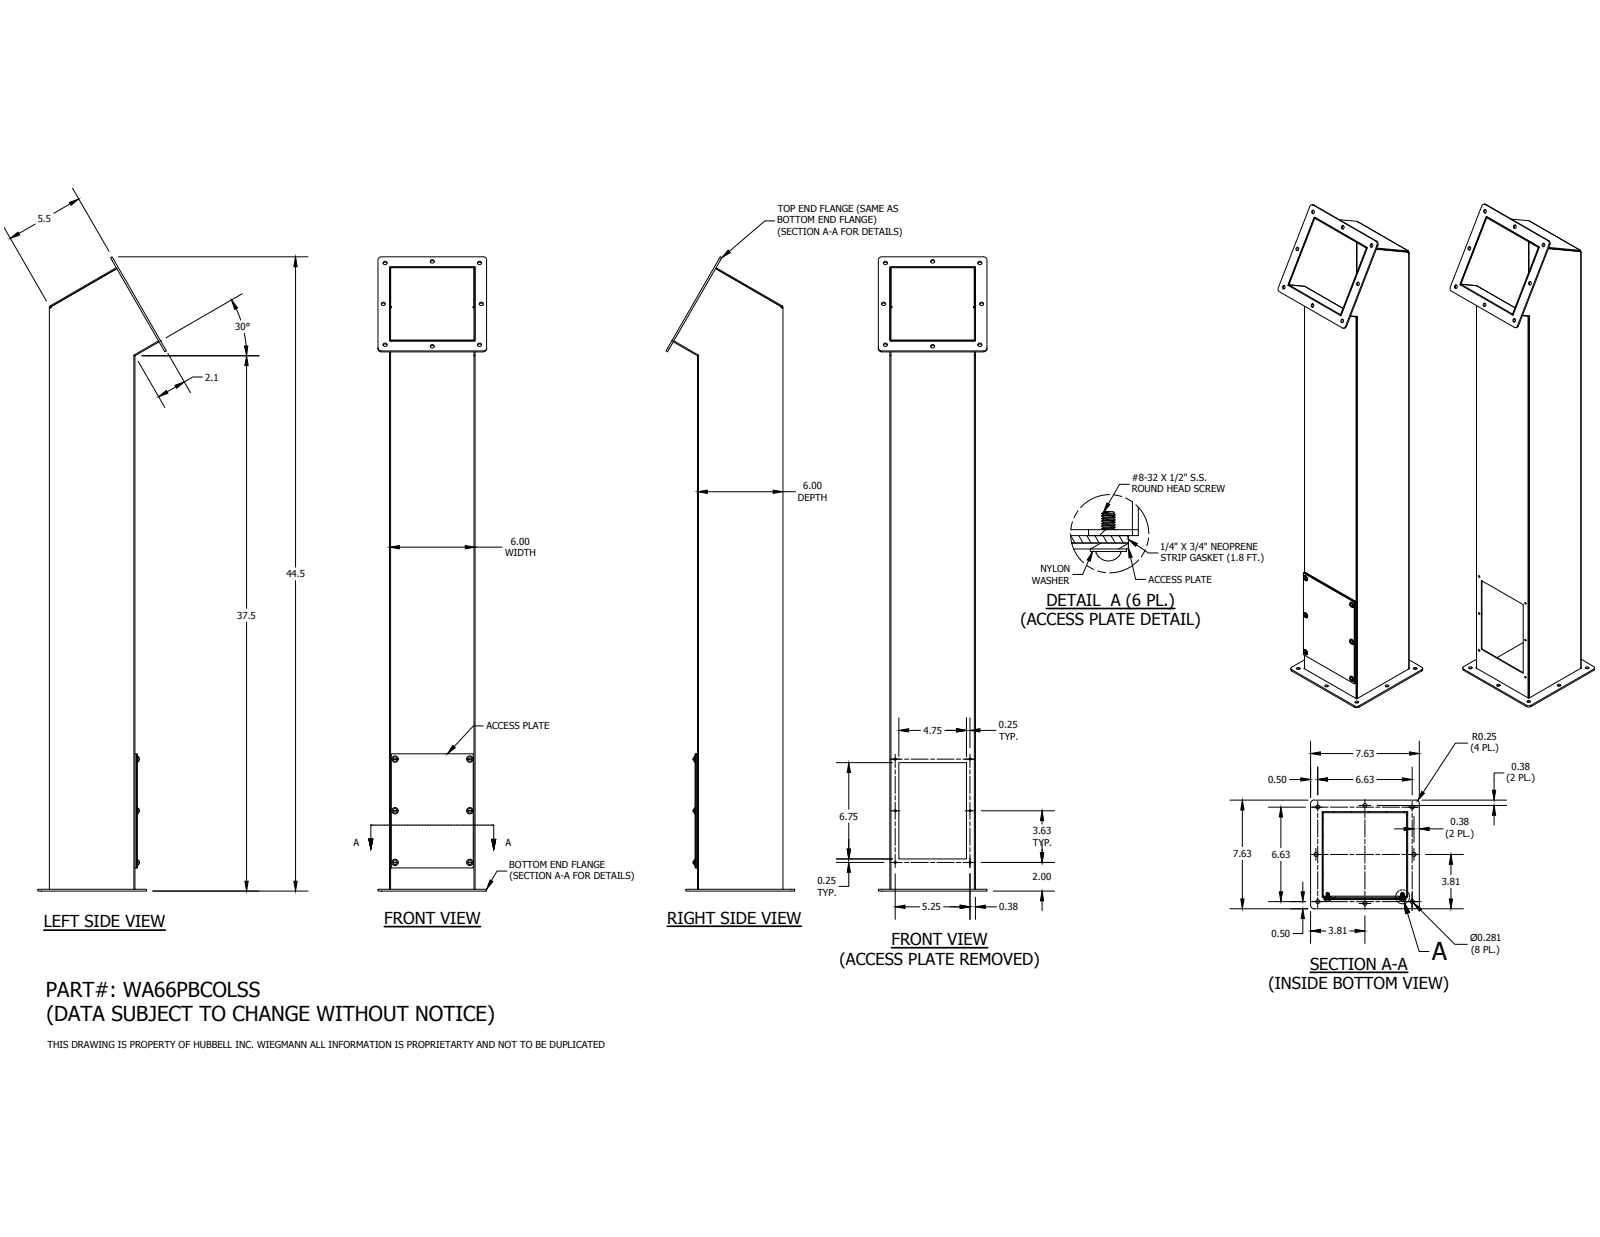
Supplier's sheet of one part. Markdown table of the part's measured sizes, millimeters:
| quantity | value |
| --- | --- |
| part name | WA66PBCOLSSFRONT; WA66PBCOLSSBLR; WA66CCOLSSBASERING; WA66CCOLSSCOVER (+4 more) |
| STEP written by | Autodesk Inventor 2016 (AUTOMOTIVE_DESIGN) |
| units | millimeters |
| bodies | 24 solids, 346 faces (202 planar, 104 cylindrical, 40 other) |
| overall size | 1129.71 × 229.15 × 193.68 |
| volume | 1 362 000 mm³ |
| surface area | 1 433 000 mm² |
| round holes (diameter × count) | 7.14 × 16, 3.56 × 6, 6.35 × 6, 7.06 × 6 |
| round bosses / shafts (diameter × count) | 11.51 × 6, 7.85 × 6, 4.17 × 6, 3.13 × 6 |
| partial cylindrical surfaces (radius × count) | 6.35 × 8, 2.27 × 6, 1.78 × 5, 0.79 × 4, 2.67 × 4 |
| main face-to-face distances | 1.88, 150.52, 152.4, 148.64, 154.78, 4.26, 152.9, 2.38, 156.66, 6.14 |
| hole center spacings | 84.2, 190.98, 168.28, 92.07, 92.08, 184.15, 123.47, 123.48 |
